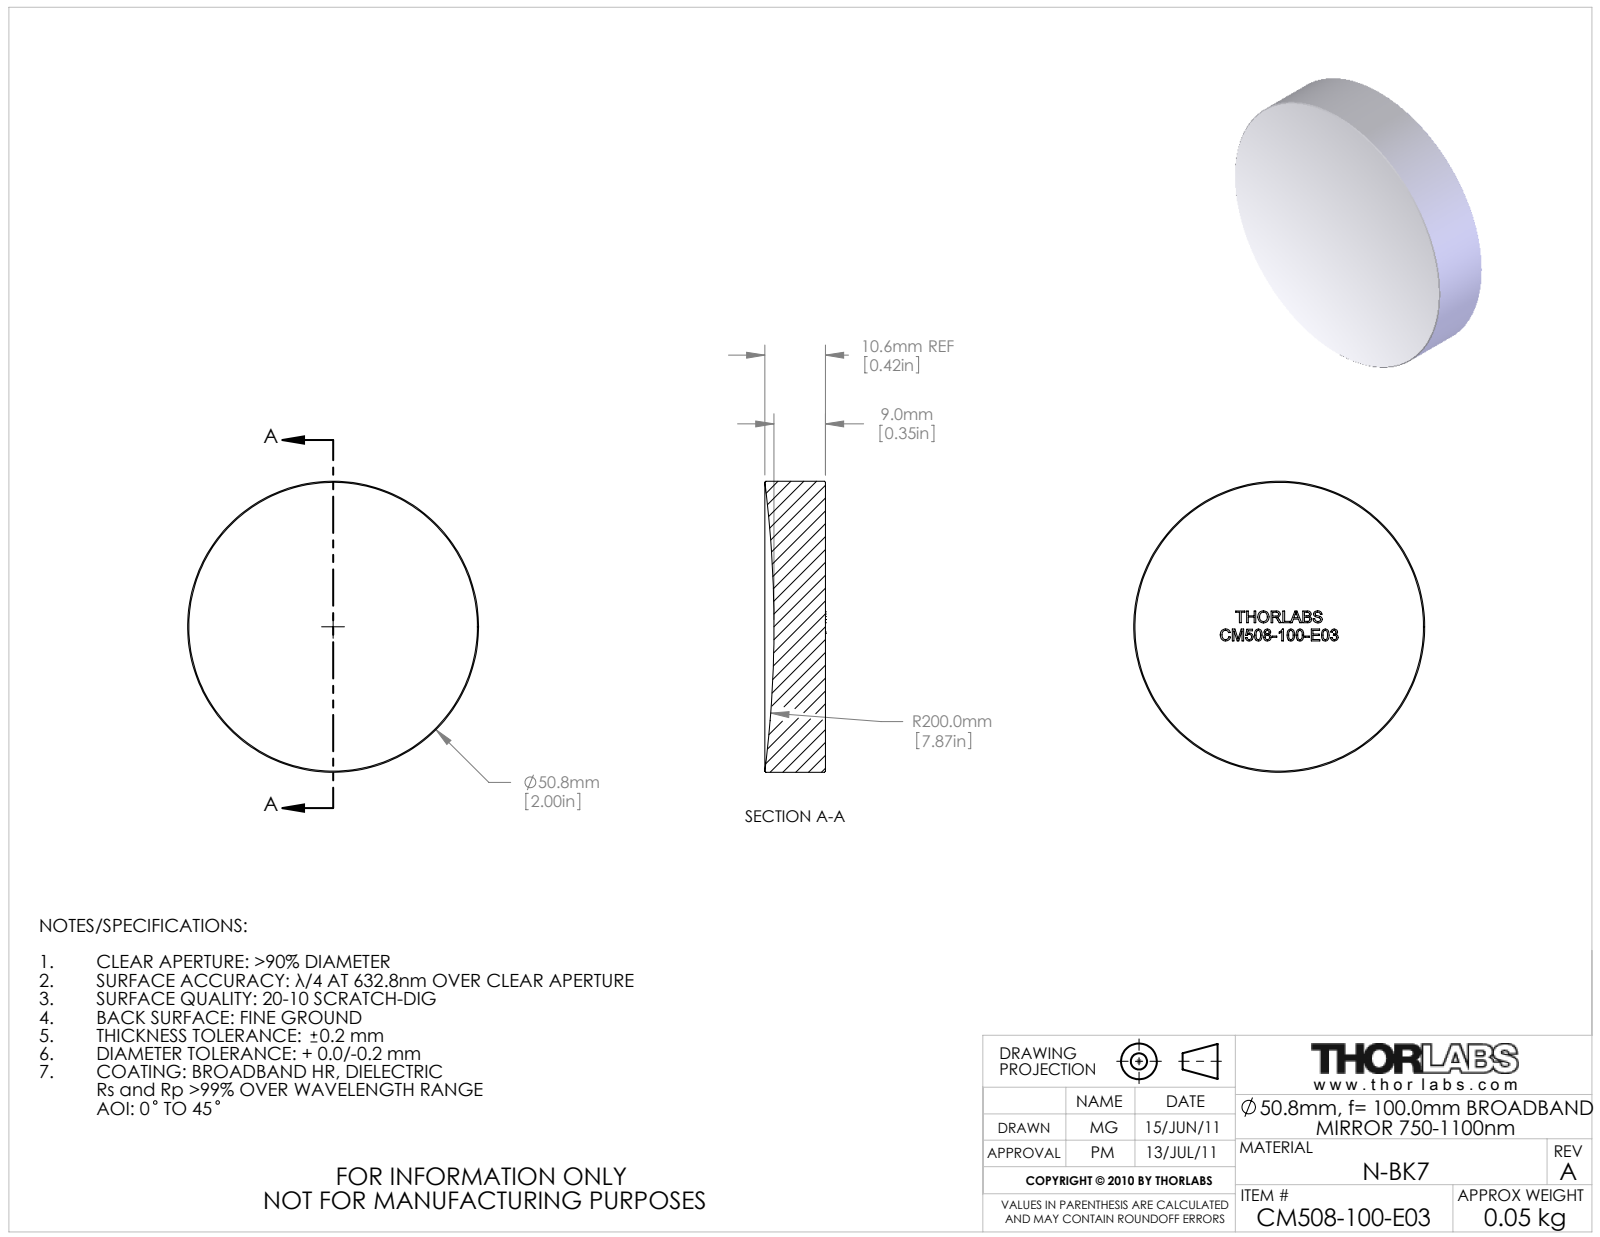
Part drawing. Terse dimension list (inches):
name: 22646-E0W
written by: SolidWorks 2011 (AUTOMOTIVE_DESIGN)
unit: in
bodies: 0 solids, 42 faces (34 planar, 2 cylindrical, 6 other)
size: 2 × 2 × 0.417
bosses: 1× ⌀2
